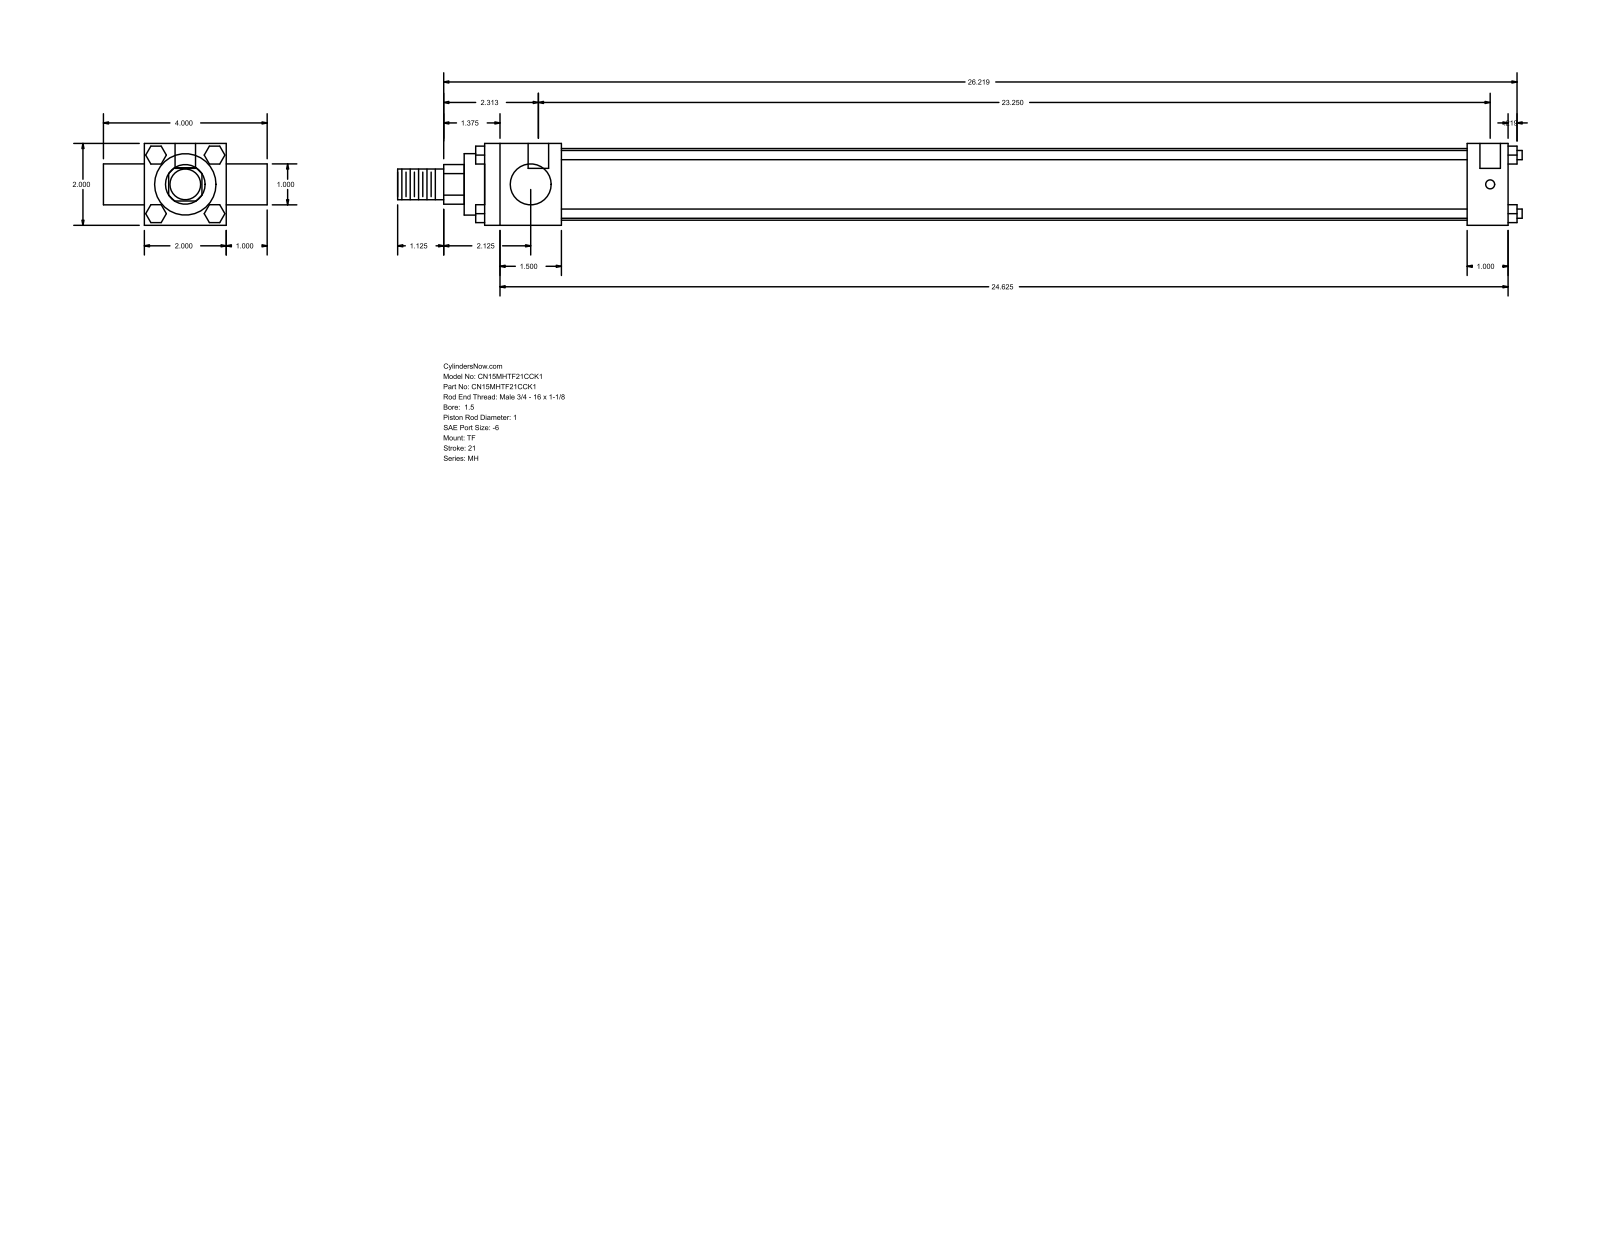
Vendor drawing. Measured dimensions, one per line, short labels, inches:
name: MH_TF__0150_1
written by: GSSL Pune (CONFIG_CONTROL_DESIGN)
unit: in
bodies: 0 solids, 120 faces (92 planar, 28 cylindrical, 0 other)
size: 27.469 × 4 × 2
holes: 3× ⌀0.219, 2× ⌀0.5
bosses: 4× ⌀0.225, 2× ⌀1, 1× ⌀1.75, 1× ⌀1.5, 1× ⌀0.75
rounds: 1× R0.484
face distances: 2, 1, 25, 3, 1.875, 23.125, 24, 22.125, 4, 0.5
hole spacings: 0.125, 23.25, 23.375
